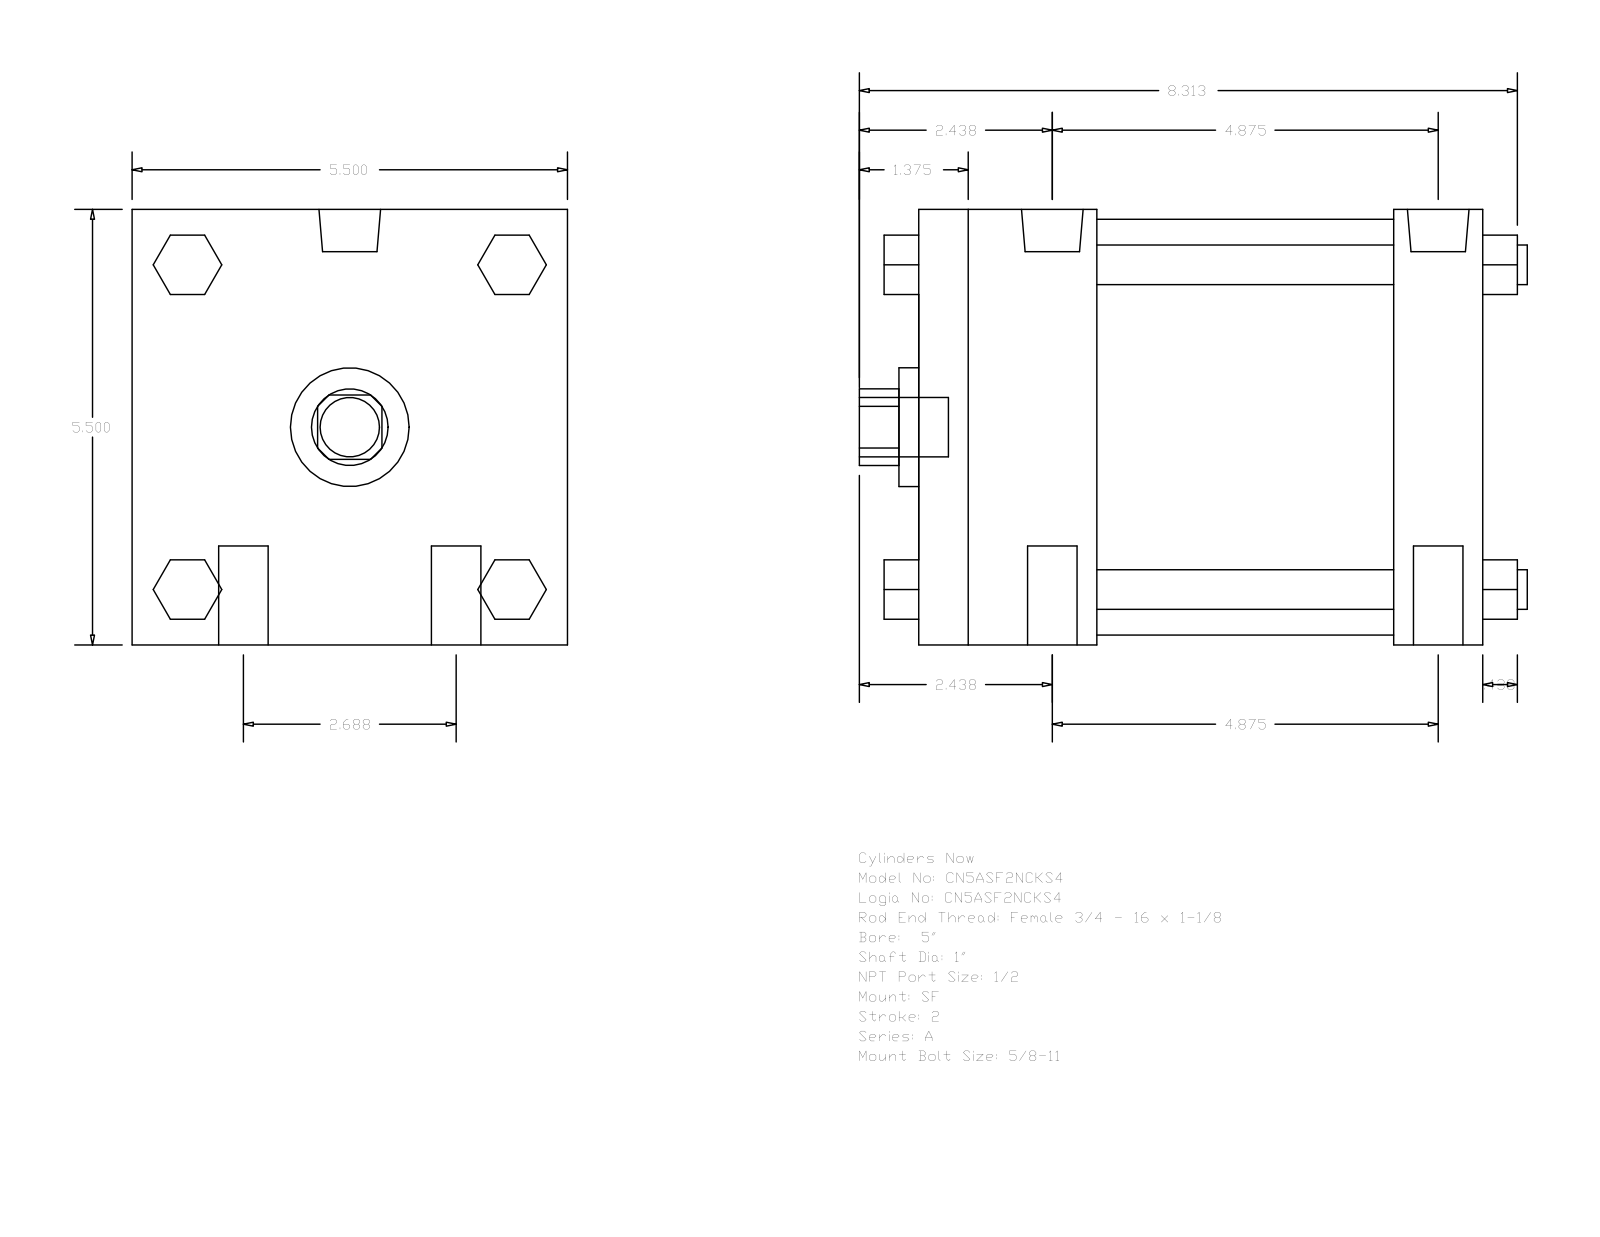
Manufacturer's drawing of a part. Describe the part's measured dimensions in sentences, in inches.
The part is named "A_SF__0500_1". Its 3-D file was written by "GSSL Pune (CONFIG_CONTROL_DESIGN)". It is 0 solids with 124 faces: 94 planar, 30 cylindrical and 0 other. Overall it measures 8.437 by 5.5 by 5.5 inches. Round holes: 1 of diameter 1, 1 of diameter 1.5, 1 of diameter 5.25. Round bosses or shafts: 4 of diameter 0.625, 4 of diameter 0.5, 2 of diameter 0.778, 2 of diameter 0.344, 1 of diameter 0.75. Partial cylindrical surfaces (rounded edges, fillets, slot ends): 1 of radius 0.484. The main face-to-face distances are 5.5, 7.125, 2.25, 6, 3.75, 4.875, 1.125, 0.75, 2.05, 3.55.
